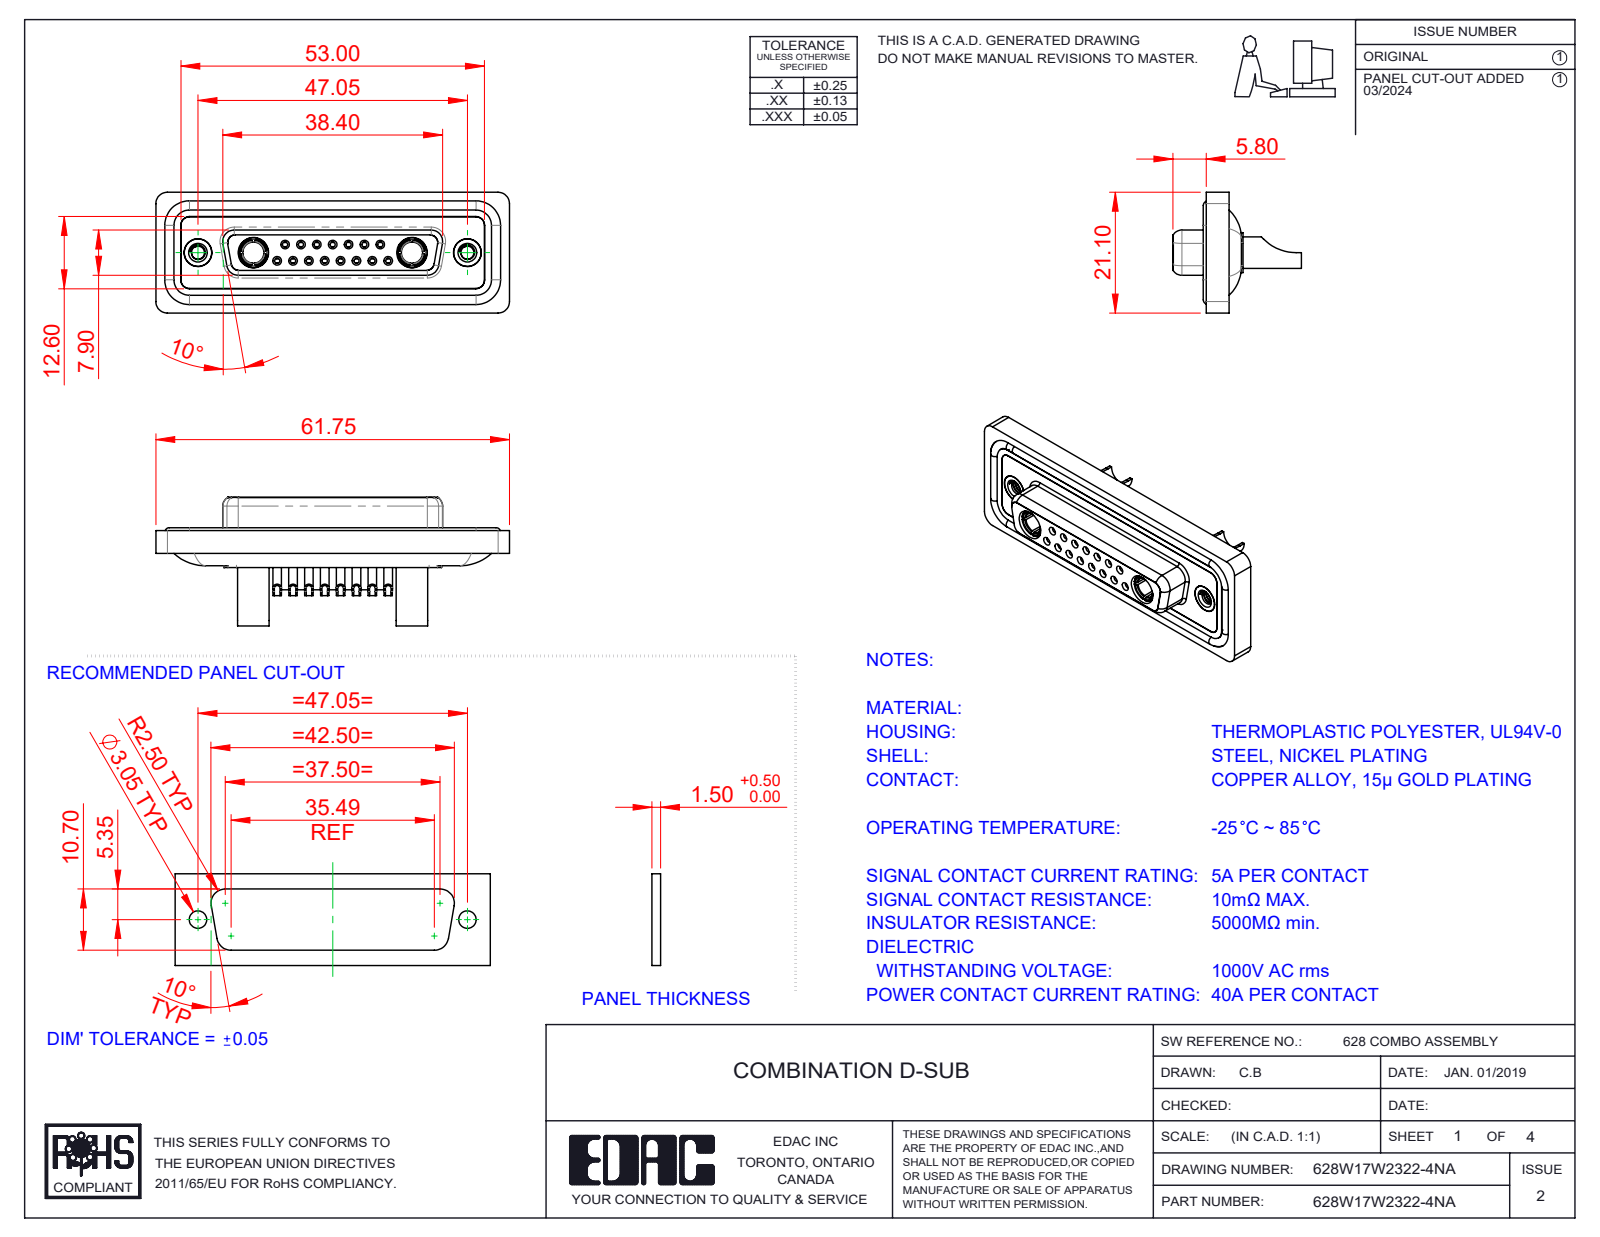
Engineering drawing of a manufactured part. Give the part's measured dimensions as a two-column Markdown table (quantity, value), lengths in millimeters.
| quantity | value |
| --- | --- |
| part name | 628Combo Contact Row 2_22; 628Combo Housing_17W2; 628Combo Shell Front_25 Contacts; 628W17W2322-4NA (+5 more) |
| STEP written by | SolidWorks 2023 (CONFIG_CONTROL_DESIGN) |
| units | millimeters |
| bodies | 26 solids, 1363 faces (422 planar, 553 cylindrical, 388 other) |
| overall size | 61.75 × 22.45 × 21.1 |
| volume | 8 437 mm³ |
| surface area | 14 292 mm² |
| round holes (diameter × count) | 0.9 × 15, 1 × 15, 1.1 × 15, 1.5 × 15, 2 × 15, 1.6 × 8, 1.7 × 7, 4.85 × 4, 2.26 × 2, 3.7 × 2, 4 × 2, 4.05 × 2 |
| round bosses / shafts (diameter × count) | 2.2 × 15, 1.6 × 11, 5.5 × 2, 5.2 × 2, 4.96 × 2, 4.95 × 2, 4.8 × 2, 4.75 × 2 |
| partial cylindrical surfaces (radius × count) | 1.5 × 22, 2 × 18, 1.35 × 8, 1.6 × 8, 1 × 6, 0.25 × 4, 0.5 × 4, 0.6 × 4 |
| main face-to-face distances | 0.4, 7.45, 1.8, 5.65, 6.6, 0.5, 7.05, 1.6, 2.9, 1.1 |
| hole center spacings | 3.16, 2.77, 8.31, 5.54, 5.03, 5.04, 7.49, 11.08 |
